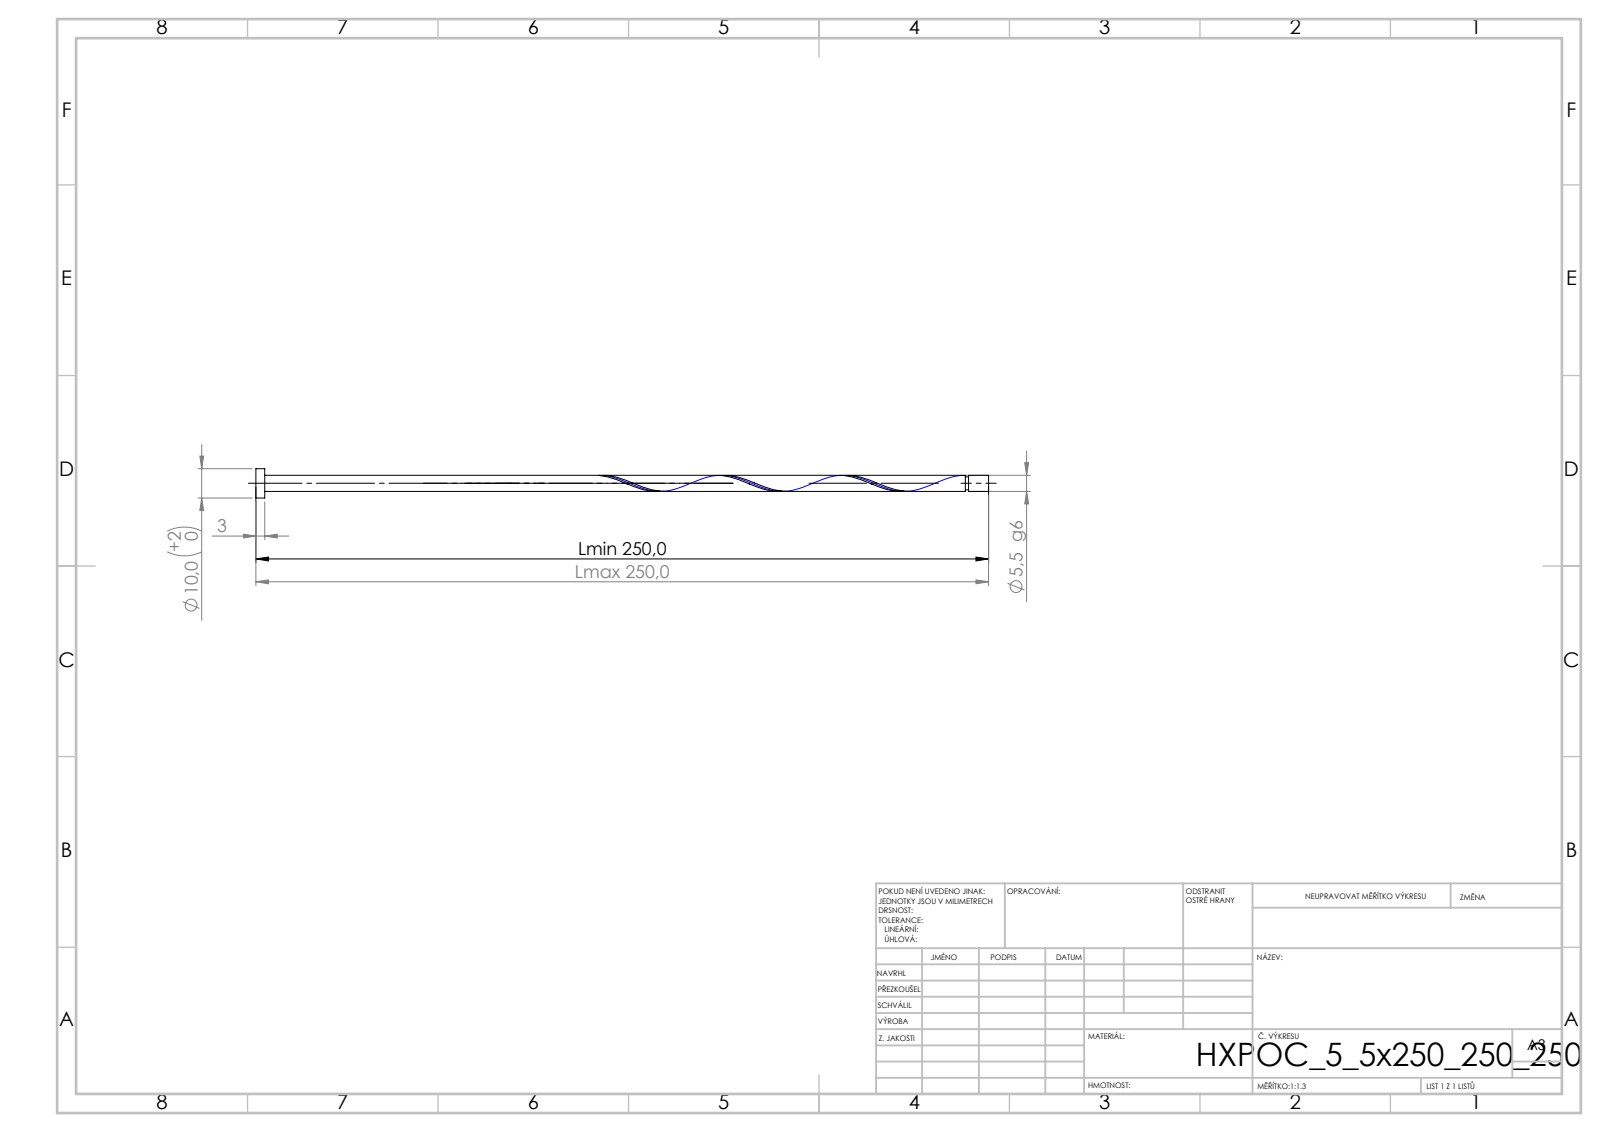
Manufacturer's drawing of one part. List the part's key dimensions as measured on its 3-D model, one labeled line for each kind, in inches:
STEP written by: SolidWorks 2019 (CONFIG_CONTROL_DESIGN)
Units: inches
Bodies: 1 solid, 21 faces (6 planar, 14 cylindrical, 1 other)
Overall size (bounding box): 9.843 × 0.394 × 0.394
Volume: 0.368 in³ · Surface area: 7.138 in²
Round bosses / shafts (diameter × count): ⌀0.394 ×1, ⌀0.217 ×1, ⌀0.173 ×1
Main face-to-face distances: 0.118, 9.843, 9.724, 9.574, 9.456, 0.269, 9.531, 9.413, 0.043, 0.312
